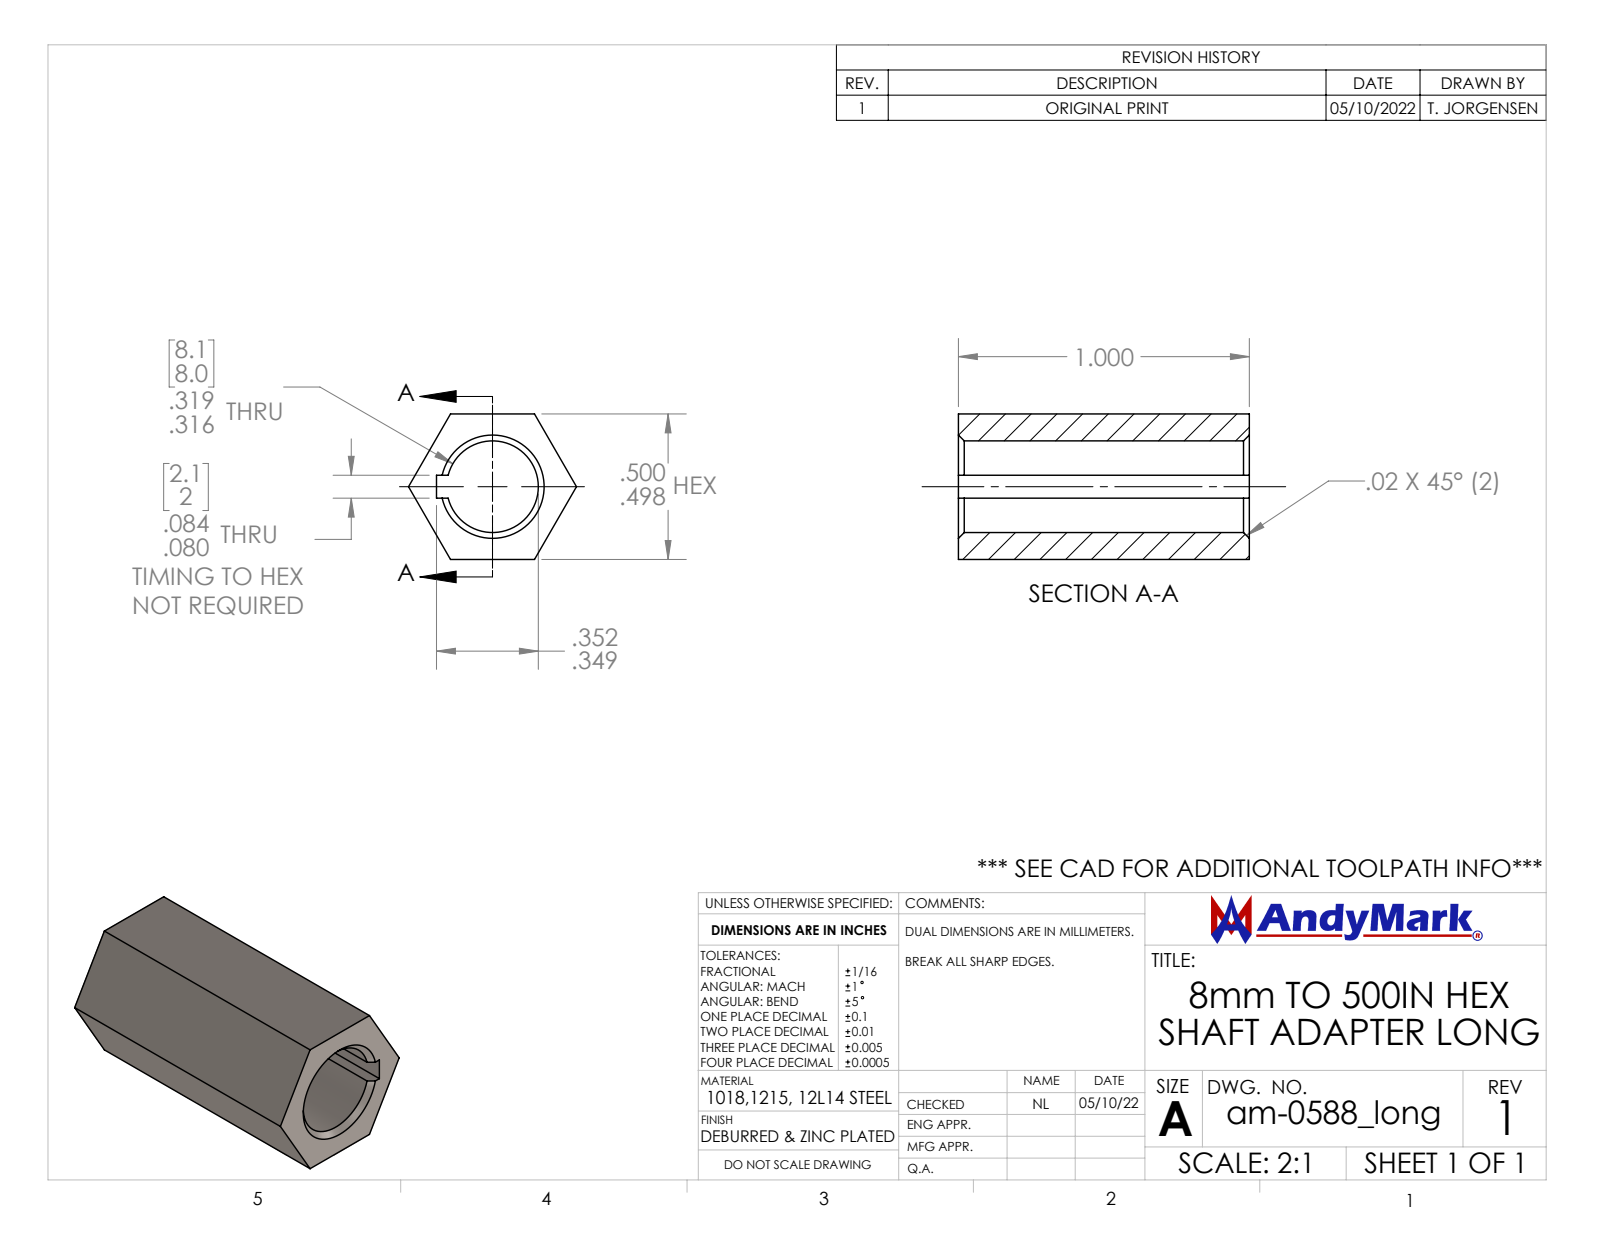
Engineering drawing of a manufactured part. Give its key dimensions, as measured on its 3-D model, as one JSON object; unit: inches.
{"part_name": "am-0588_long 8mm 500 Hex Adapter Shaft 1000 long", "step_written_by": "SolidWorks 2024 (AUTOMOTIVE_DESIGN)", "units": "inches", "bodies": {"solids": 1, "faces": 32, "planar": 11, "cylindrical": 3, "other": 18}, "overall_size": [1, 0.577, 0.5], "volume_in3": 0.135, "surface_area_in2": 3.022, "round_holes": [[0.315, 1]], "face_to_face_distances": [0.5, 1, 0.211, 0.289, 0.079]}
